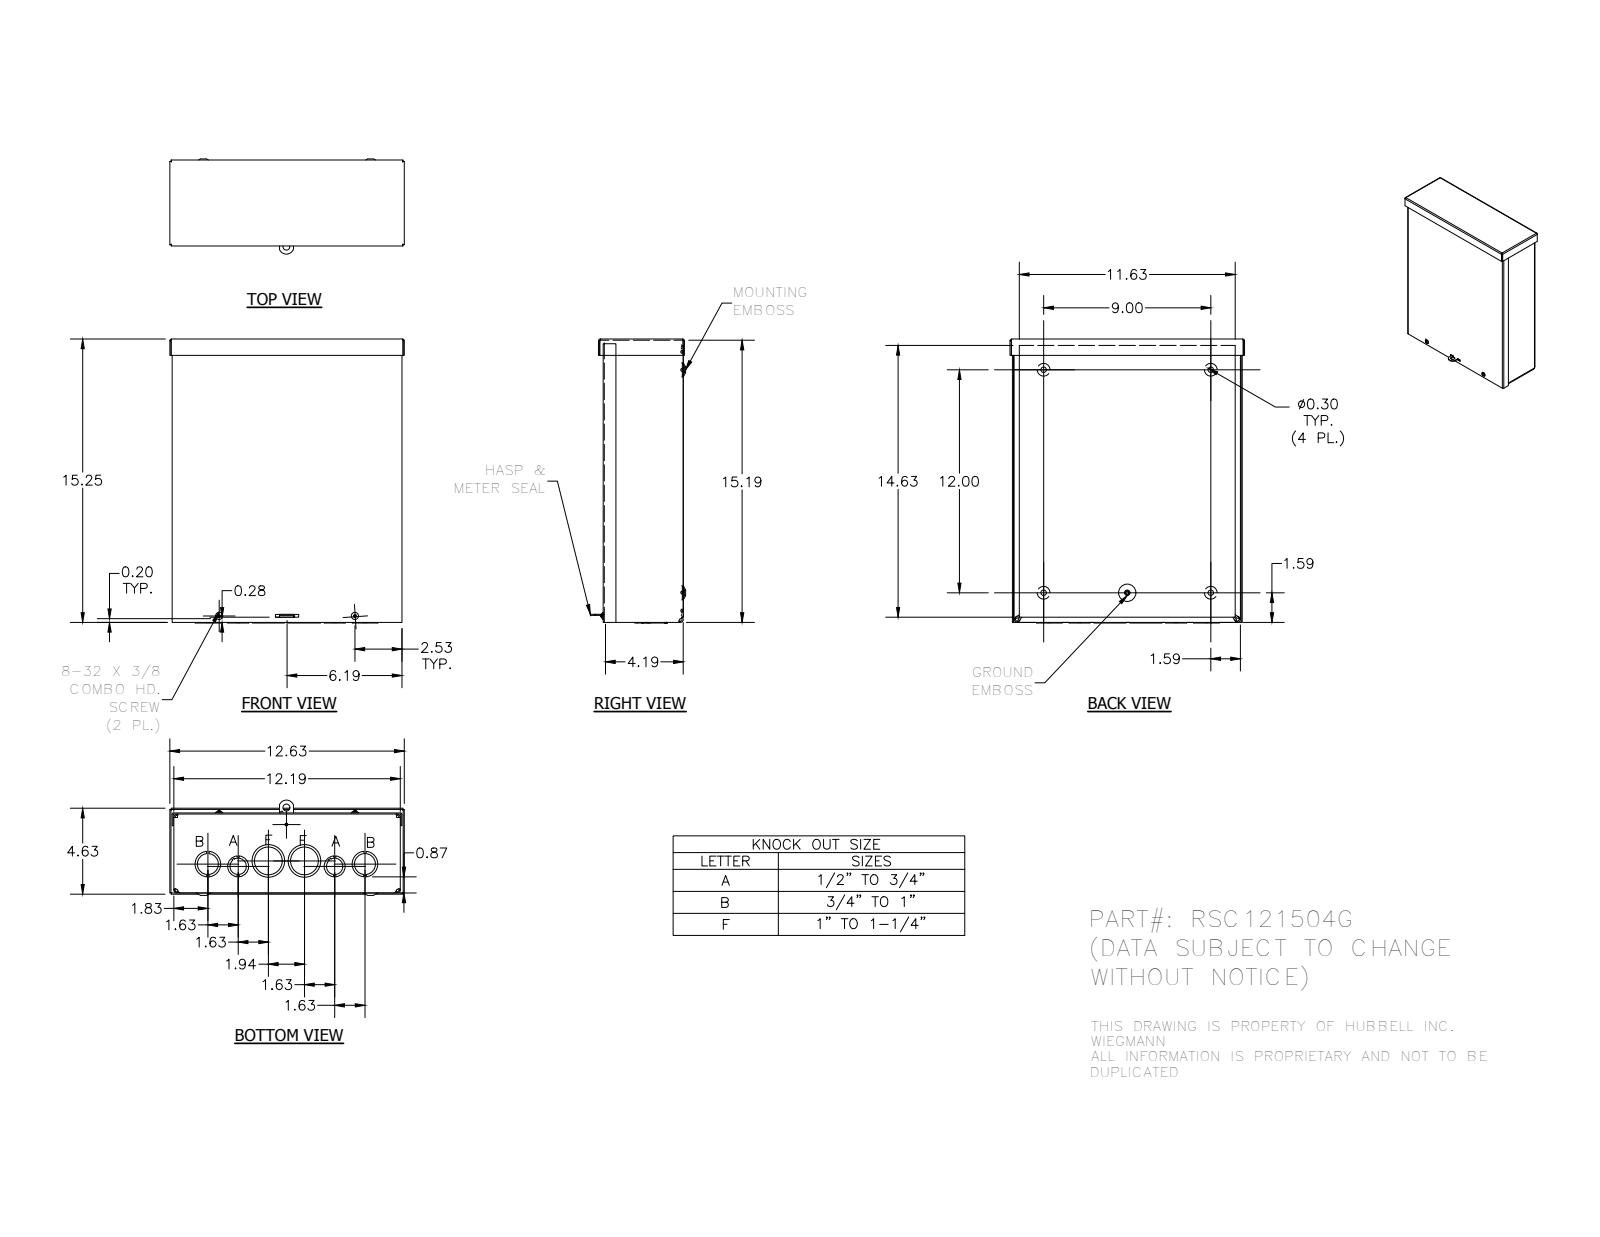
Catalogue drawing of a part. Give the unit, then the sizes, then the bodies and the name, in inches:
Units: inches
Overall size (bounding box): 15.28 × 12.625 × 5.125
Round holes (diameter × count): ⌀0.3 ×4, ⌀0.313 ×4, ⌀1.125 ×4, ⌀0.125 ×2, ⌀0.148 ×2, ⌀0.875 ×2, ⌀1.375 ×2, ⌀1.5 ×2, ⌀1.75 ×2, ⌀0.156 ×1, ⌀0.165 ×1, ⌀0.375 ×1
Round bosses / shafts (diameter × count): ⌀0.384 ×2, ⌀0.164 ×2, ⌀0.228 ×1
Partial cylindrical surfaces — rounded edges, fillets, slot ends (radius × count): R0.01 ×14, R0.031 ×8, R0.093 ×8, R0.125 ×8, R0.187 ×8, R0.031 ×6, R0.025 ×5, R0.055 ×4
Main face-to-face distances: 0.062, 4.249, 4.187, 0.063, 4.312, 4.25, 0.062, 12.126, 0.124, 15.126
Hole centre spacings: 1.356, 1.635, 1.656, 3.031, 3.264, 3.582, 4.5, 5.203
Volume: 47.36 in³ · Surface area: 1 547 in²
Bodies: 7 solids, 551 faces (264 planar, 143 cylindrical, 144 other)
Part name (STEP PRODUCT): RSC121504G_WRAP; RSC1215G_LID; RSC1204G_CAP; 3183 (+4 more)
STEP written by: Autodesk Inventor 2014 (AUTOMOTIVE_DESIGN)
